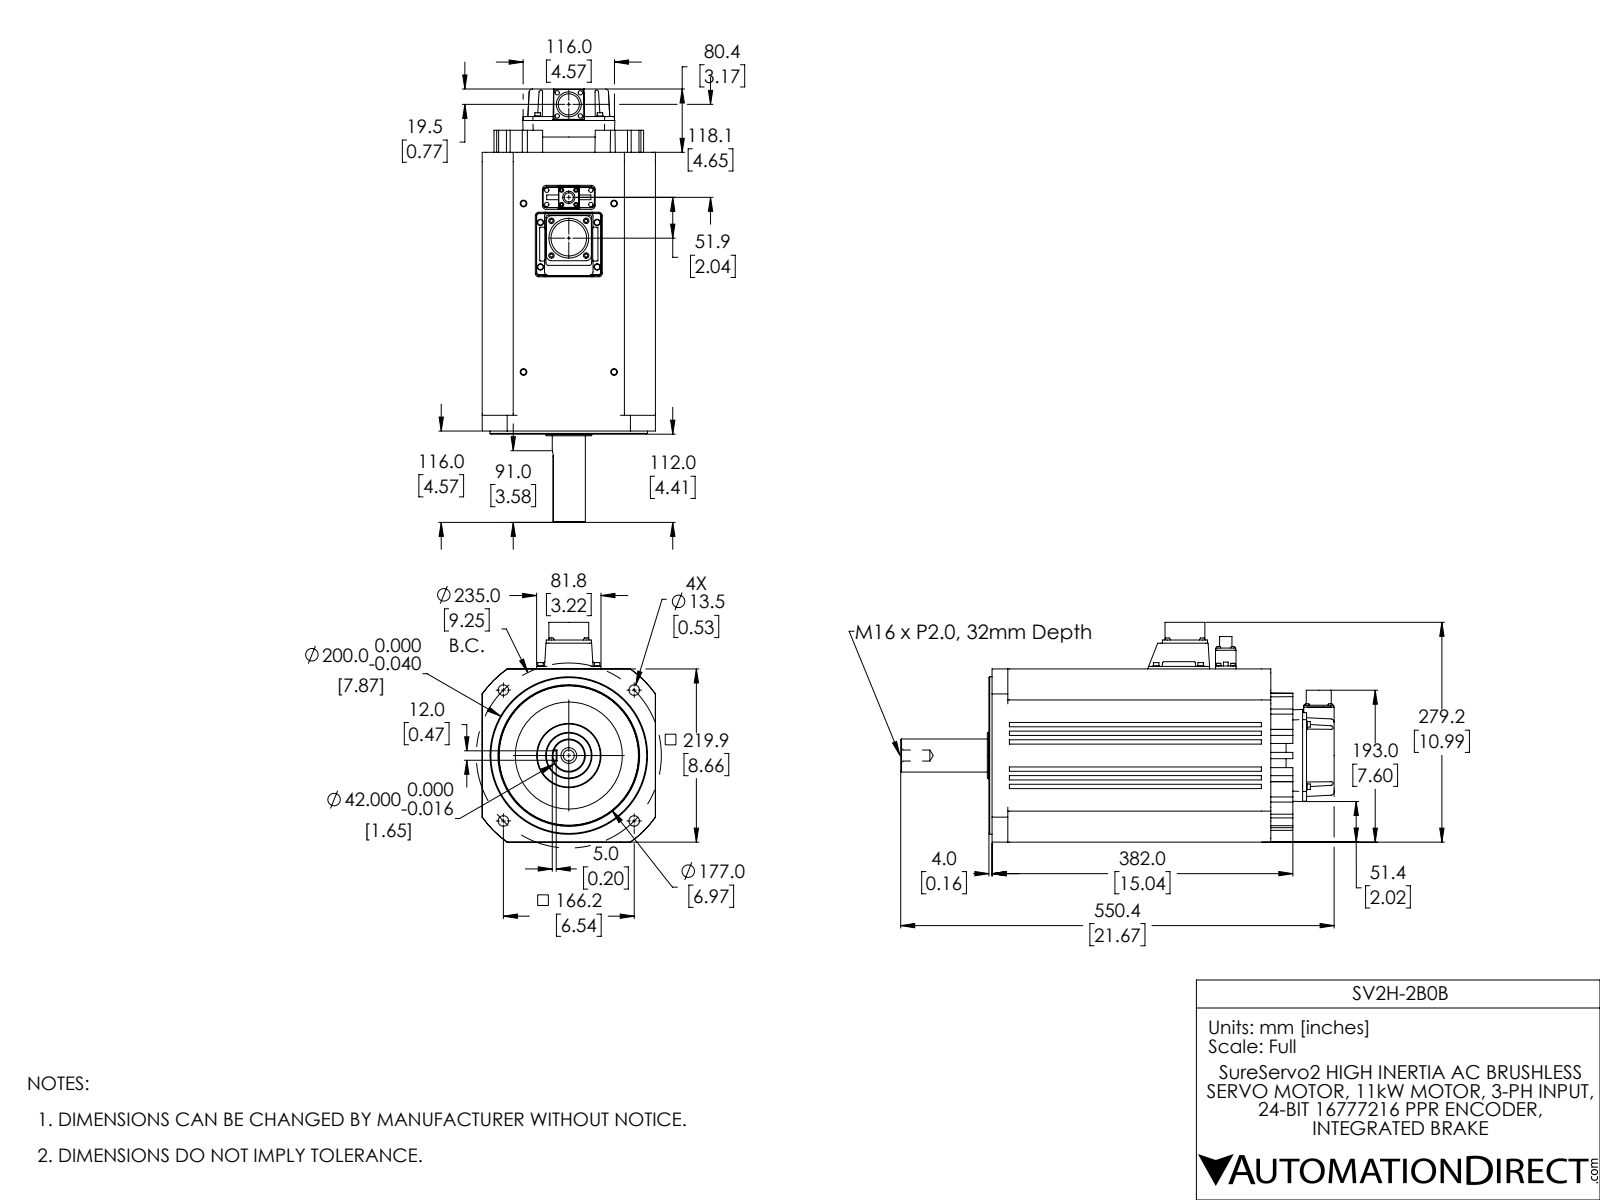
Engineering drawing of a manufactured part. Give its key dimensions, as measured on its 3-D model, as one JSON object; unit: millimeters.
{"part_name": "SV2H-2B0B", "step_written_by": "SolidWorks 2017 (AUTOMOTIVE_DESIGN)", "units": "millimeters", "bodies": {"solids": 1, "faces": 809, "planar": 405, "cylindrical": 261, "other": 143}, "overall_size": [550.5, 279.2, 220], "volume_mm3": 16210000, "surface_area_mm2": 591200, "round_holes": [[4.3, 4], [4.6, 4], [6.8, 4], [13.5, 4], [11.7, 1], [14, 1], [26.9, 1], [45.3, 1], [180, 1]], "round_bosses_or_shafts": [[8, 8], [7, 8], [6, 4], [5.5, 4], [4, 4], [200, 1], [178, 1], [136, 1]], "partial_cylinders_radius": [[0.5, 32], [5, 28], [3, 20], [4, 16], [1, 4], [2, 4], [4.5, 4], [5.5, 4]], "face_to_face_distances": [220, 39.4, 180.6, 5.5, 11, 141.2, 62, 16.5, 56.5, 67.5], "hole_center_spacings": [117.5, 166.2, 32.3, 41.2, 48.1, 51.3, 56.5, 58]}
